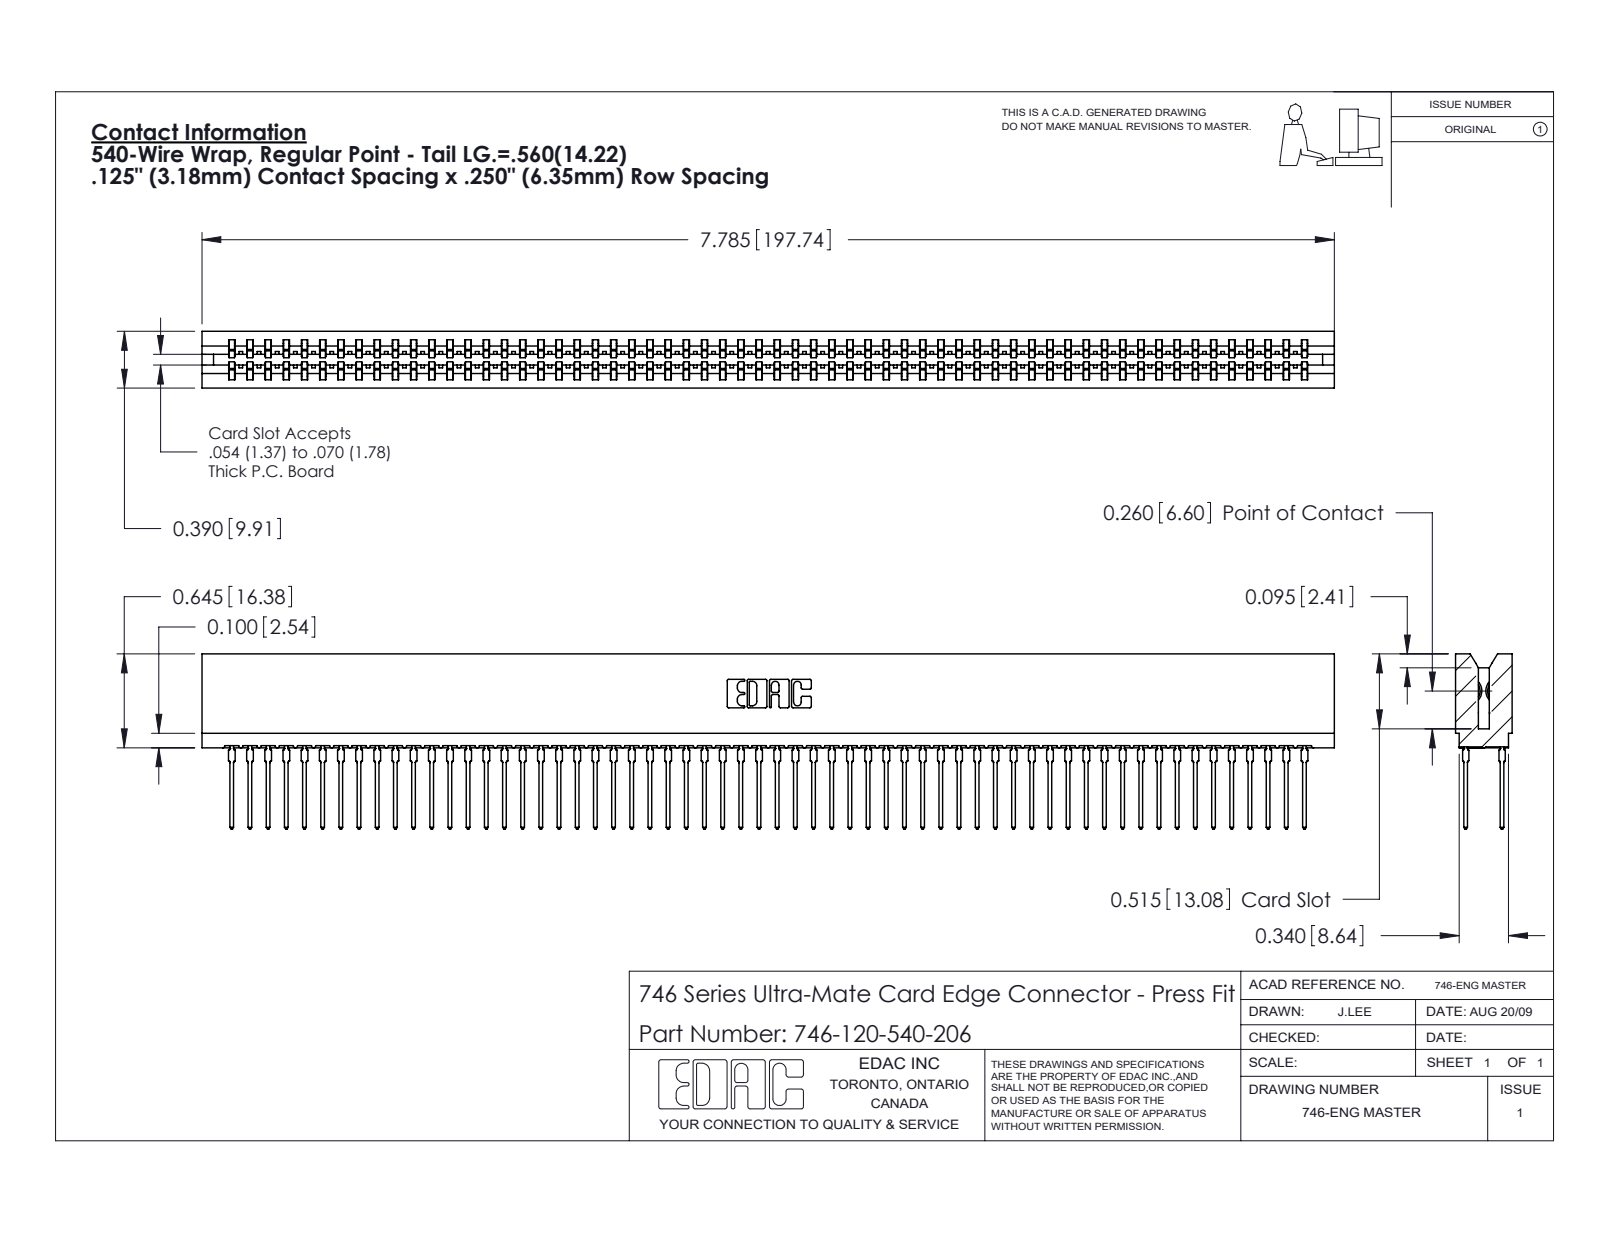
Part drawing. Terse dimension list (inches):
name: 746 Part_.515 Slot Depth - 06; 746-120-540-206; 746-292-001_540
written by: SolidWorks 2020 (CONFIG_CONTROL_DESIGN)
unit: in
bodies: 121 solids, 10838 faces (5576 planar, 2142 cylindrical, 3120 other)
size: 7.785 × 1.204 × 0.39
volume: 1.308 in³; area: 56.51 in²
rounds: 240× R0.021, 61× R0.015, 22× R0.01, 8× R0.005, 8× R0.011, 6× R0.007, 6× R0.031, 3× R0.026
face distances: 0.057, 0.333, 0.25, 0.39, 0.025, 0.307, 0.083, 0.275, 0.174, 0.158
